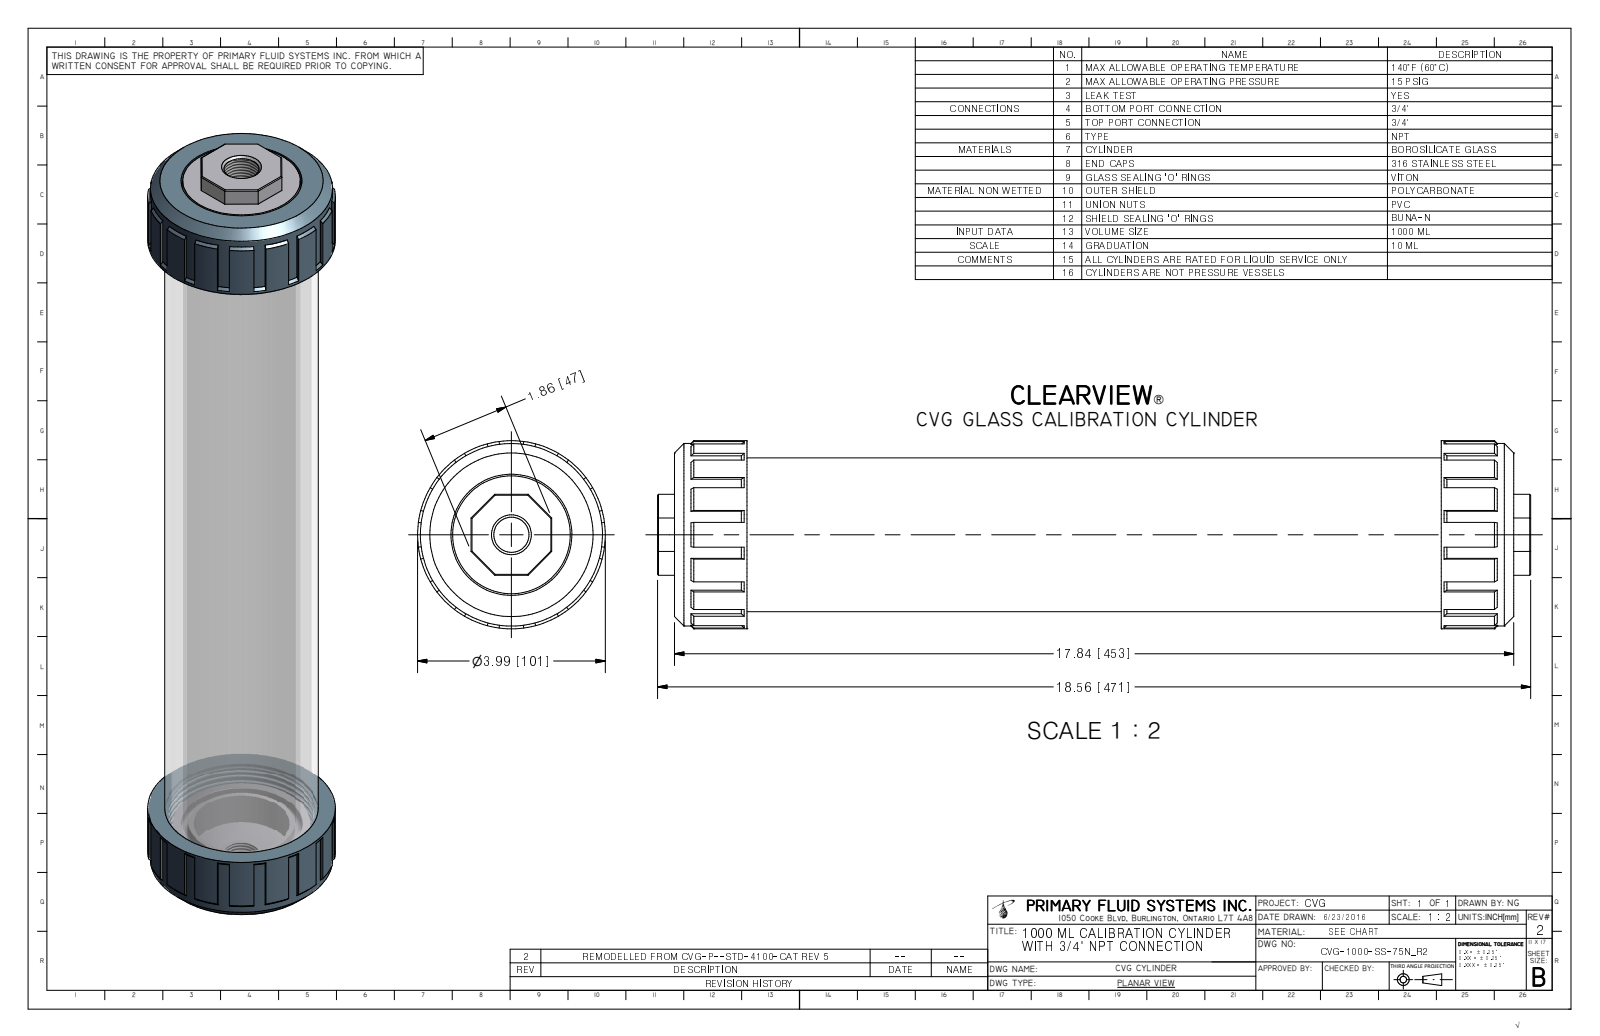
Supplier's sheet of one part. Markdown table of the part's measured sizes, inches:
| quantity | value |
| --- | --- |
| part name | CVG-1000-SS-75N_R2; CVG-3-1000-METAL-NPT-75_R4; CVG-1-1000-A_R0; CVG-6-1000 (+1 more) |
| STEP written by | Autodesk Inventor 2009 (AUTOMOTIVE_DESIGN) |
| units | inches |
| bodies | 6 solids, 320 faces (134 planar, 67 cylindrical, 119 other) |
| overall size | 18.56 × 3.99 × 3.99 |
| volume | 56.55 in³ |
| surface area | 760.7 in² |
| round holes (diameter × count) | 0.747 × 1, 2.052 × 1, 2.331 × 1, 2.57 × 1, 2.585 × 1, 2.985 × 1, 3.147 × 1, 3.265 × 1, 3.265 × 1 |
| round bosses / shafts (diameter × count) | 3.99 × 1, 3.87 × 1, 3.225 × 1, 3.107 × 1, 3.087 × 1, 2.935 × 1, 2.801 × 1, 2.52 × 1 |
| main face-to-face distances | 1.54, 16.3, 17.84, 0.3, 17.54, 1.24, 16, 14.76, 0.36, 0.66 |
